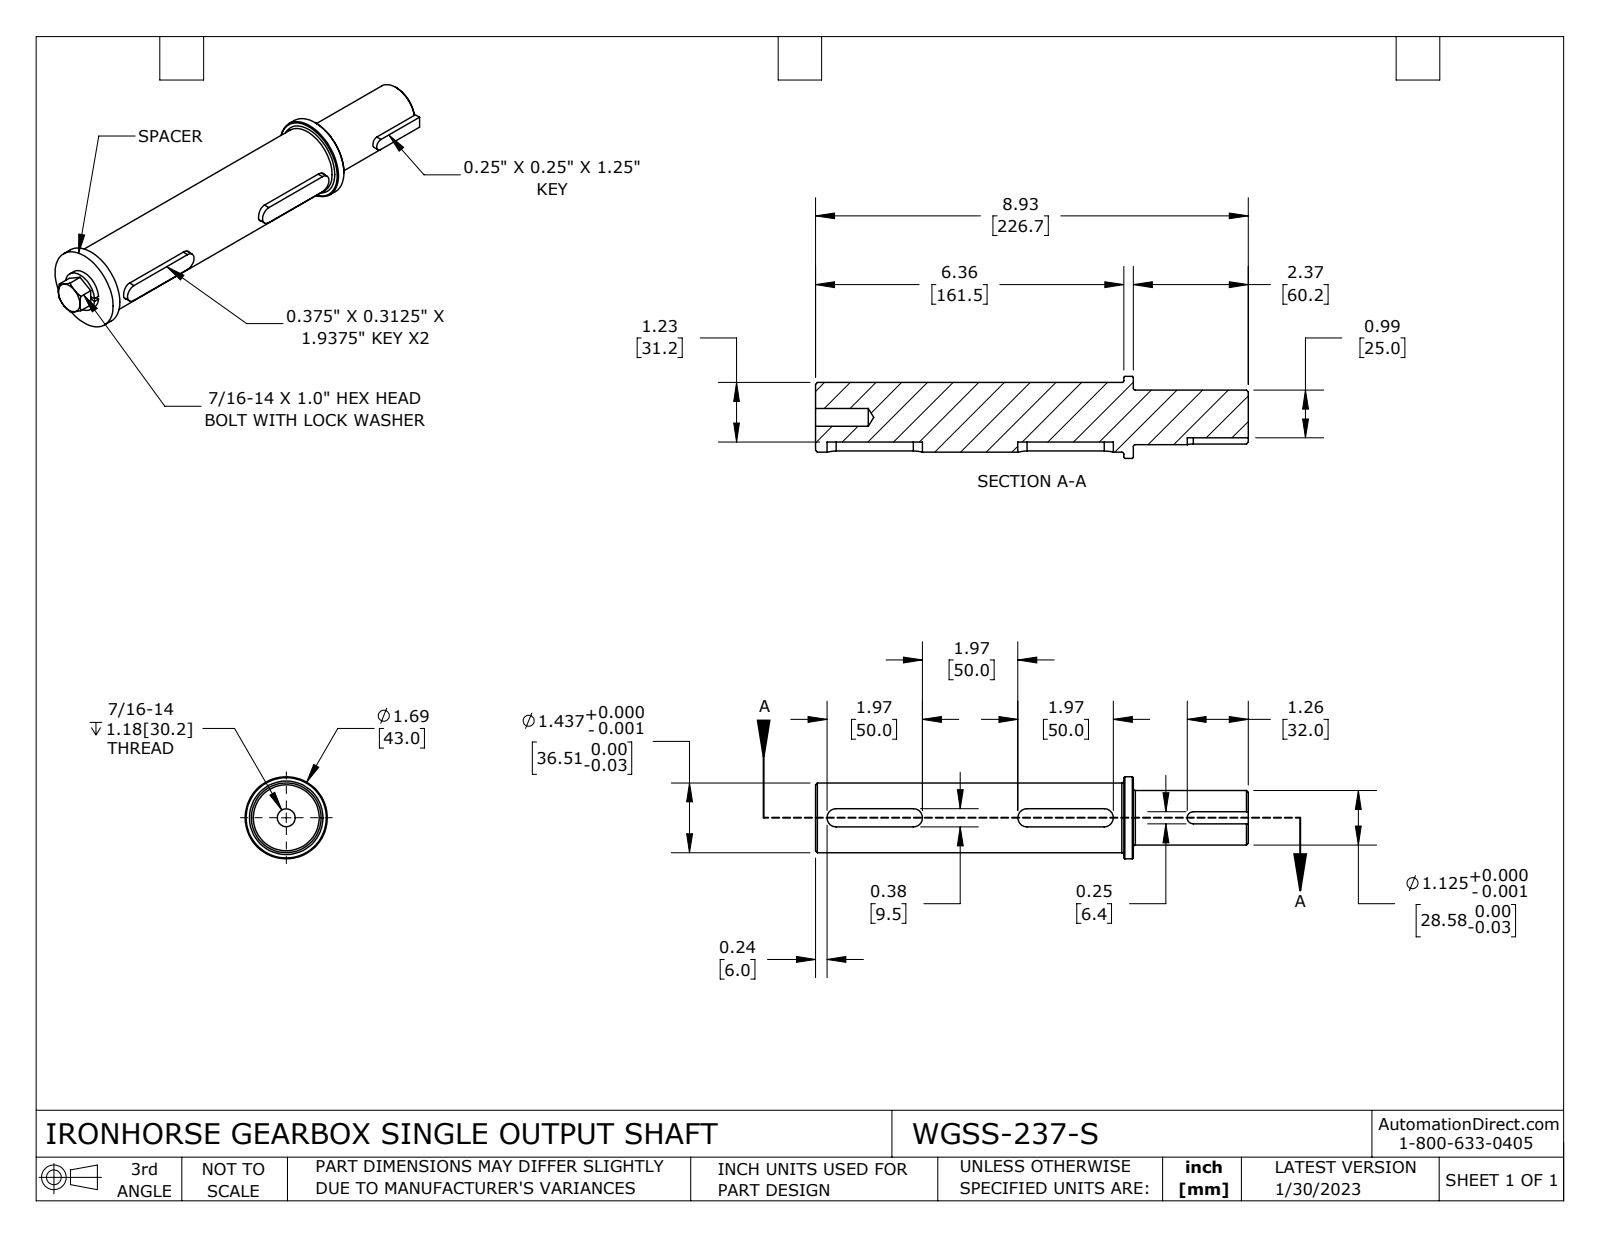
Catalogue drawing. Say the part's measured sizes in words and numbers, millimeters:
The part is named "WGSS-237-S". Its 3-D file was written by "SolidWorks 2021 (CONFIG_CONTROL_DESIGN)". It is 7 solids with 93 faces: 41 planar, 31 cylindrical and 21 other. Overall it measures 242.7 by 43 by 43 millimeters. Its volume is 227 500 cubic millimeters and its surface area 39 780 square millimeters. Round holes: 1 of diameter 9.3, 1 of diameter 12, 1 of diameter 12.2. Round bosses or shafts: 1 of diameter 43, 1 of diameter 36.5, 1 of diameter 28.6, 1 of diameter 21.5, 1 of diameter 11.1. Partial cylindrical surfaces (rounded edges, fillets, slot ends): 4 of radius 4.8, 4 of radius 4.8, 1 of radius 3.2. The main face-to-face distances are 5, 8, 166.5, 171.5, 9.5, 1.6, 231.7, 226.7, 60.2, 6.4.
